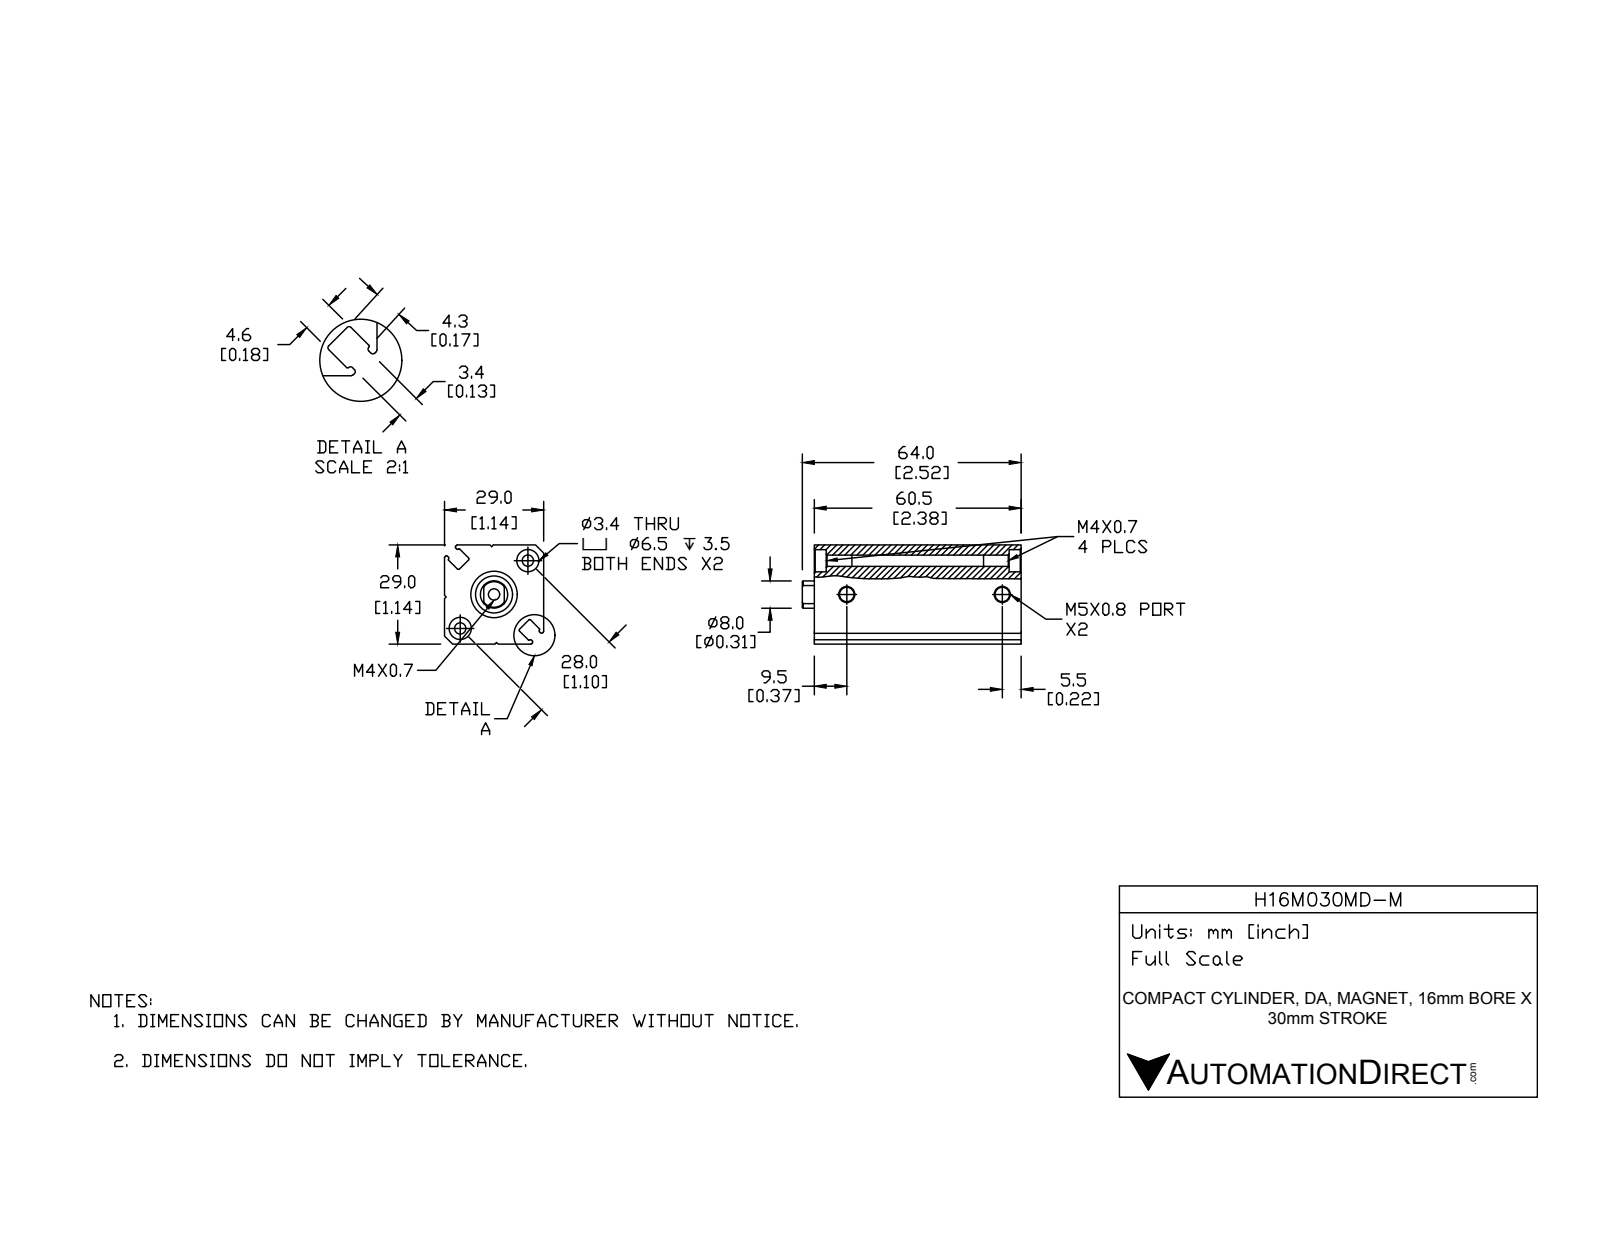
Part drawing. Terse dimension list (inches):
name: H16M030MD-M; H16M030MD-M-BODY; H16M030MD-M-PISTON
written by: SolidWorks 2015 (CONFIG_CONTROL_DESIGN)
unit: in
bodies: 2 solids, 128 faces (49 planar, 54 cylindrical, 25 other)
size: 2.52 × 1.142 × 1.142
volume: 2.47 in³; area: 25.78 in²
holes: 3× ⌀0.13, 2× ⌀0.165, 2× ⌀0.256, 1× ⌀0.315, 1× ⌀0.535, 1× ⌀0.63
bosses: 1× ⌀0.425
rounds: 16× R0.016, 4× R0.008
face distances: 1.142, 2.382, 0.157, 0.181, 2.224, 0.651, 0.832, 0.978, 1.483, 0.795
hole spacings: 0.551, 1.102, 1.791
